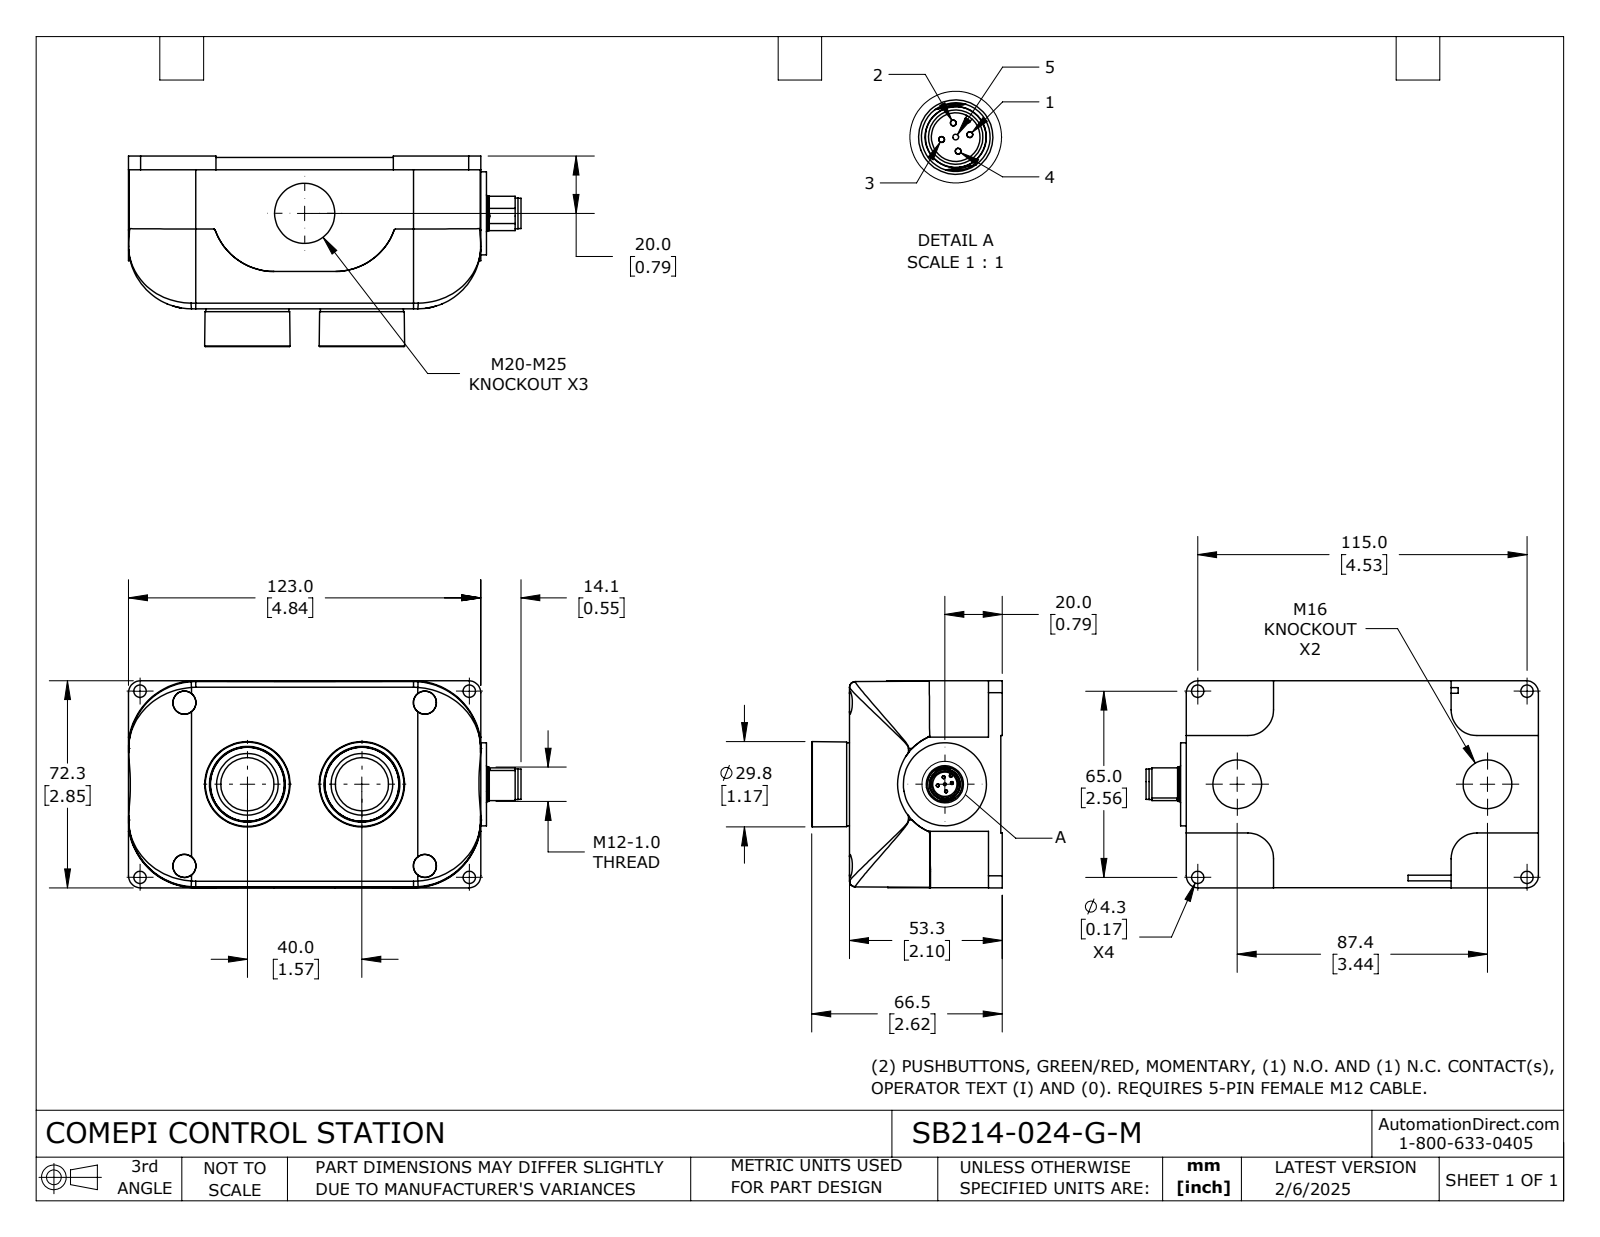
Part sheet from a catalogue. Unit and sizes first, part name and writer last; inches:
Units: inches
Overall size (bounding box): 5.396 × 2.846 × 2.618
Round holes (diameter × count): ⌀0.04 ×4, ⌀0.067 ×4, ⌀0.087 ×4, ⌀0.169 ×4, ⌀0.531 ×2, ⌀0.669 ×2, ⌀0.827 ×2, ⌀0.854 ×2, ⌀0.335 ×1
Round bosses / shafts (diameter × count): ⌀0.039 ×5, ⌀0.085 ×4, ⌀0.065 ×4, ⌀1.142 ×3, ⌀1.016 ×2, ⌀0.748 ×2, ⌀0.63 ×2, ⌀0.614 ×2
Partial cylindrical surfaces — rounded edges, fillets, slot ends (radius × count): R0.02 ×5, R0.01 ×4, R0.035 ×4, R0.079 ×4, R0.157 ×4, R0.354 ×4, R0.38 ×4, R0.866 ×4
Main face-to-face distances: 0.098, 2.079, 1.98, 0.118, 0.976, 0.878, 1.102, 2.098, 0.02, 2.618
Hole centre spacings: 1.39, 1.954, 3.309, 4.185, 0.098, 0.139, 0.139, 0.933
Volume: 16.54 in³ · Surface area: 129.7 in²
Bodies: 14 solids, 665 faces (255 planar, 235 cylindrical, 175 other)
Part name (STEP PRODUCT): SB214-024-G-M
STEP written by: SolidWorks 2024 (CONFIG_CONTROL_DESIGN)
